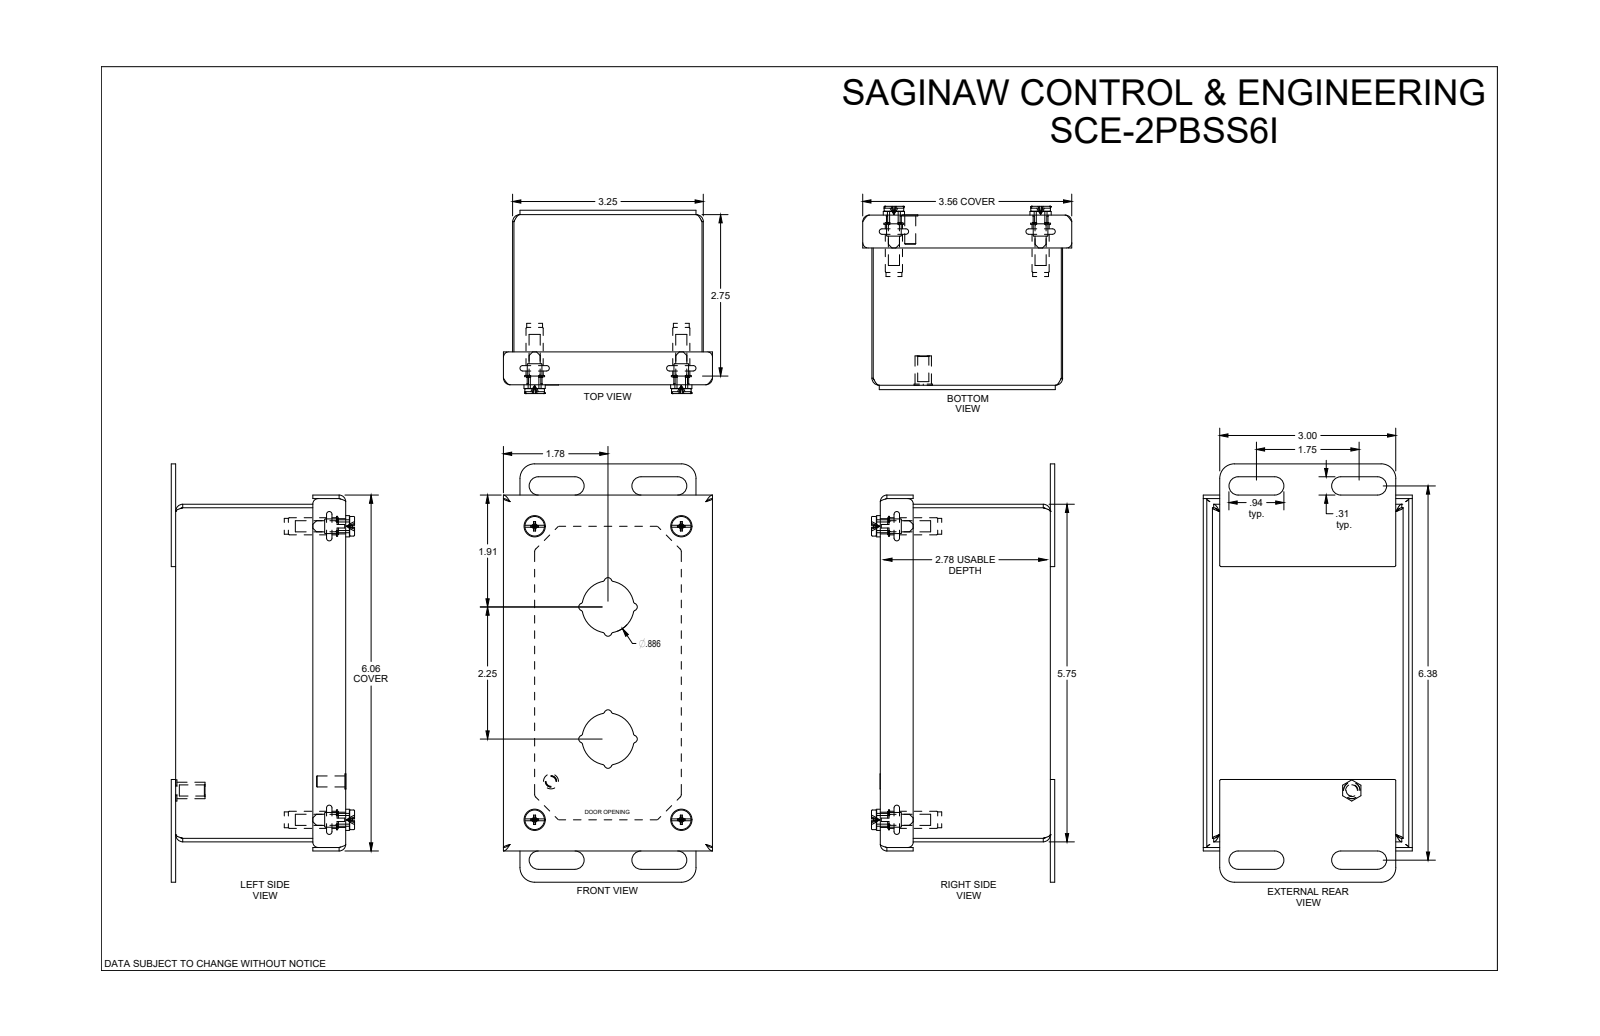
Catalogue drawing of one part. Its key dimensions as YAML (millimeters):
part_name: "SCE-2PBI"
step_written_by: "SolidWorks 2021 (AUTOMOTIVE_DESIGN)"
units: millimeters
bodies: {solids: 12, faces: 371, planar: 139, cylindrical: 100, other: 132}
overall_size: [181, 90.5, 79.3]
volume: 112400
surface_area: 147900
round_holes:
  - {diameter: 5.6, count: 4}
round_bosses_or_shafts:
  - {diameter: 9.2, count: 4}
  - {diameter: 8.5, count: 4}
  - {diameter: 6.6, count: 4}
  - {diameter: 4.8, count: 4}
  - {diameter: 3.7, count: 4}
partial_cylinders:
  - {radius: 1.5, count: 20}
  - {radius: 1, count: 16}
  - {radius: 1.6, count: 14}
  - {radius: 4, count: 8}
  - {radius: 0.5, count: 4}
  - {radius: 6.4, count: 4}
  - {radius: 11.3, count: 4}
  - {radius: 1.6, count: 2}
face_to_face_distances: [1.5, 72.1, 81, 73.6, 70.6, 144.5, 82.6, 79.5, 68.3, 3.8]
hole_center_spacings: [63.5, 127, 142]
